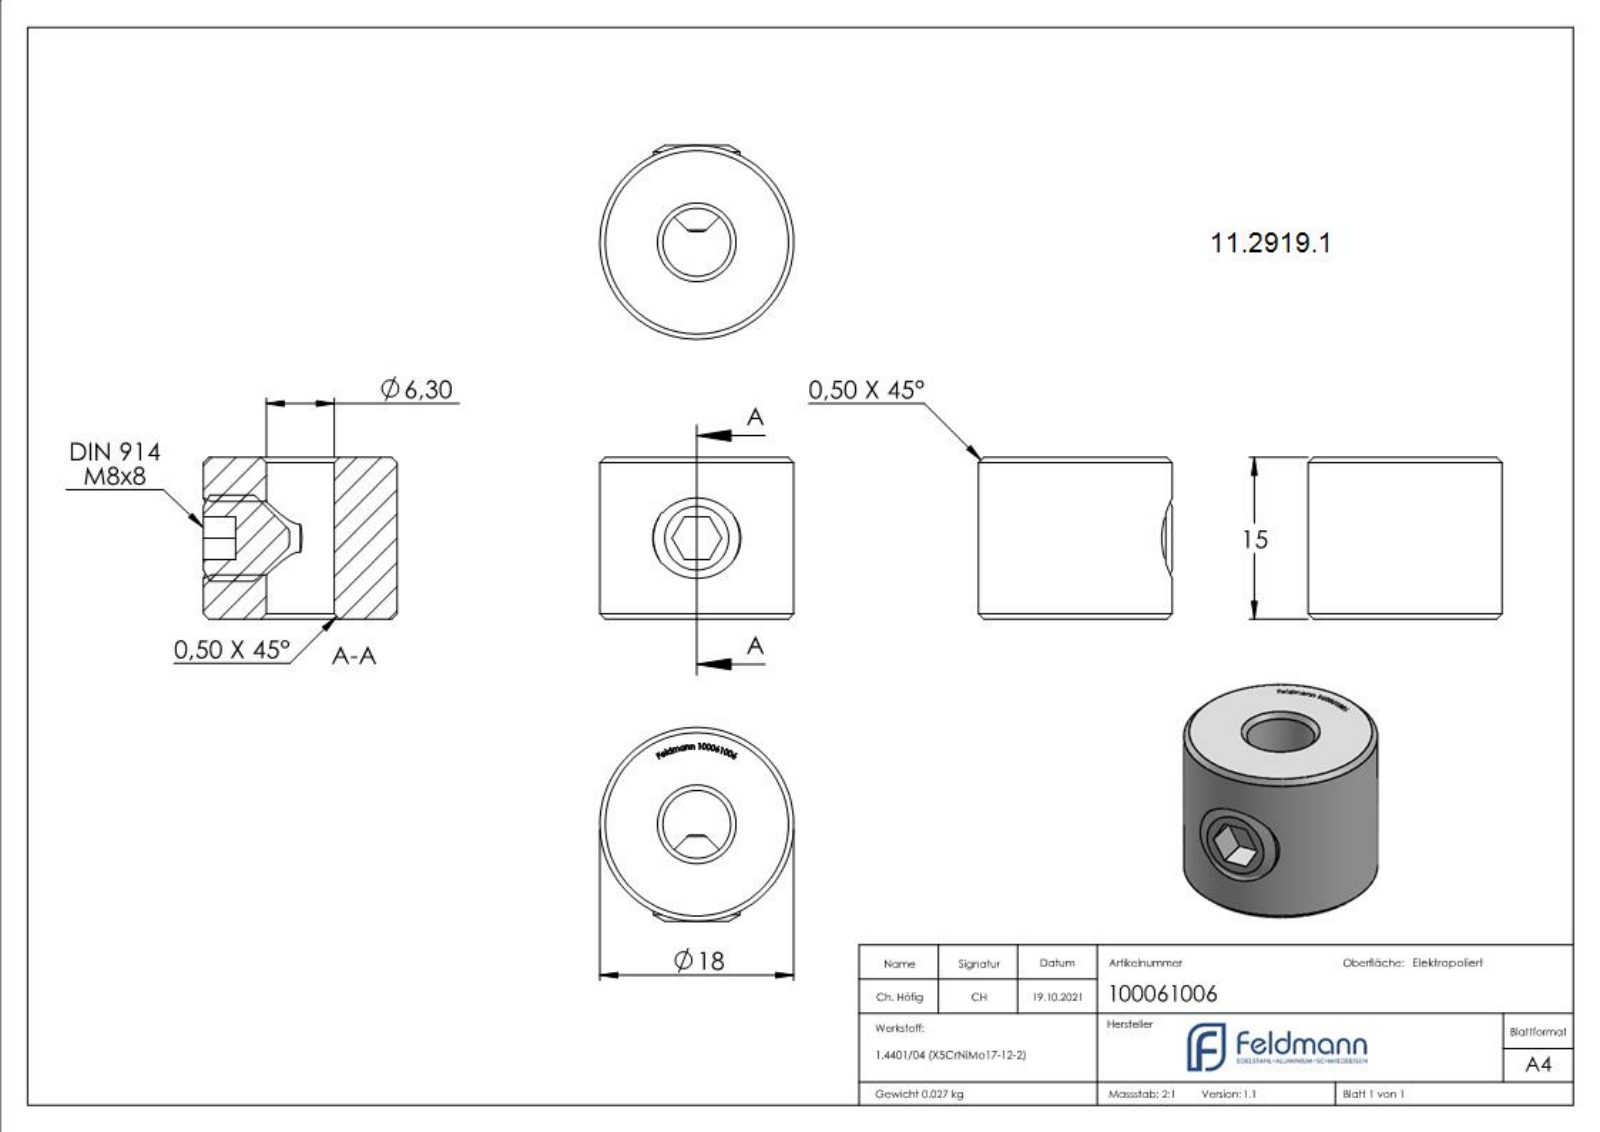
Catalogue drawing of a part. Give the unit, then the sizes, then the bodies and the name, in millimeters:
Units: millimetres
Overall size (bounding box): 18 × 18 × 15
Round holes (diameter × count): ⌀6.3 ×1, ⌀6.8 ×1
Round bosses / shafts (diameter × count): ⌀18 ×1, ⌀8 ×1
Main face-to-face distances: 15, 4, 5.5, 9.5, 3, 14.9, 9.4, 5.4, 5, 8
Volume: 3 354 mm³ · Surface area: 1 873 mm²
Bodies: 2 solids, 250 faces (110 planar, 8 cylindrical, 132 other)
Part name (STEP PRODUCT): 100061006; 10006100X Teil1_100061006 Teil1; DIN914_DIN 914 M8x8
STEP written by: SolidWorks 2015 (CONFIG_CONTROL_DESIGN)
